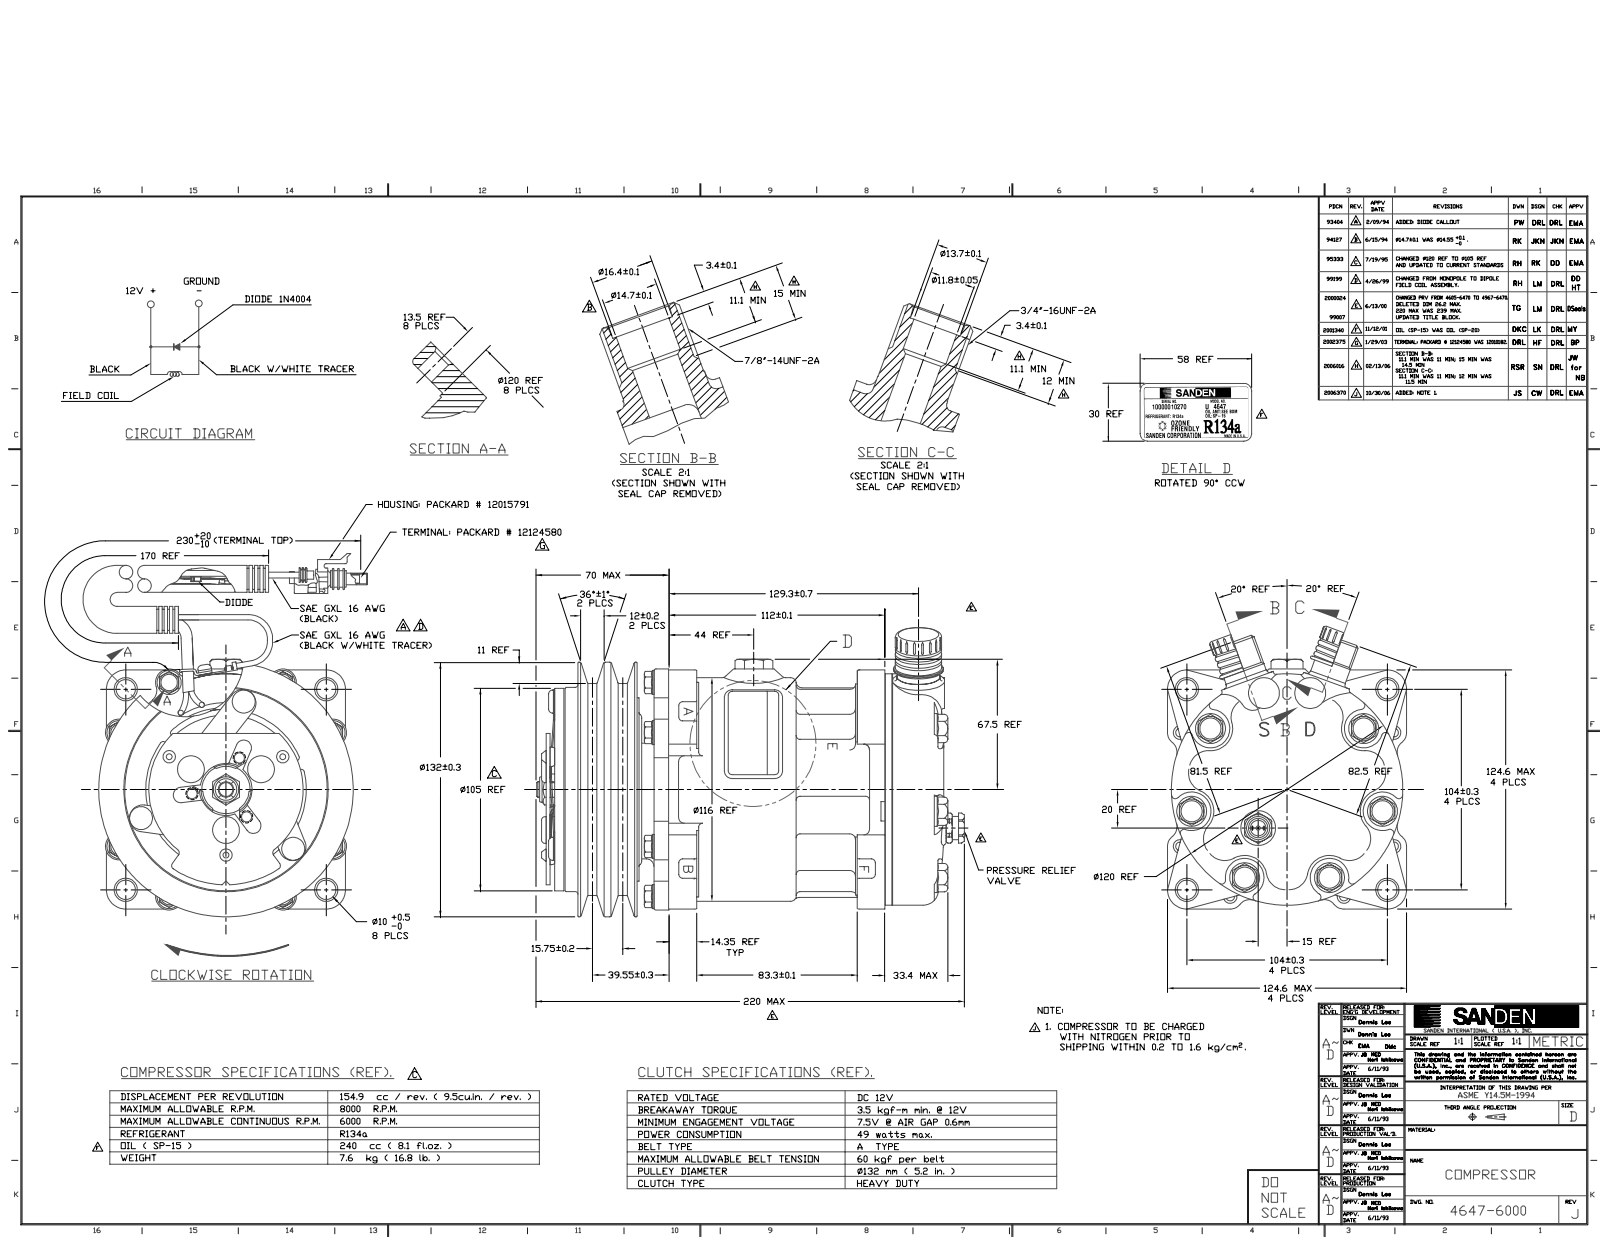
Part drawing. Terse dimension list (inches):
name: SANDEN_4647_REV_L_COMPR_AC1
written by: SolidWorks 2010 (CONFIG_CONTROL_DESIGN)
unit: in
bodies: 3 solids, 2424 faces (682 planar, 717 cylindrical, 1025 other)
size: 14.264 × 8.658 × 5.197
volume: 129.7 in³; area: 397 in²
holes: 8× ⌀0.217, 8× ⌀0.276, 8× ⌀0.335, 6× ⌀0.469, 4× ⌀0.404, 3× ⌀0.087, 3× ⌀0.2, 3× ⌀0.26, 3× ⌀0.315, 1× ⌀0.138, 1× ⌀0.197, 1× ⌀0.465
bosses: 8× ⌀0.508, 8× ⌀0.224, 6× ⌀0.602, 5× ⌀0.106, 4× ⌀0.472, 3× ⌀0.551, 3× ⌀0.394, 3× ⌀0.311
rounds: 33× R0.079, 33× R0.276, 26× R0.039, 24× R0.256, 22× R0.118, 19× R0.197, 18× R0.059, 13× R0.157
face distances: 0.22, 0.252, 0.197, 0.079, 1.832, 1.572, 1.769, 1.99, 1.517, 1.738
hole spacings: 0.896, 2.474, 3.212, 3.5, 4.324, 5.311, 1.827, 1.448
